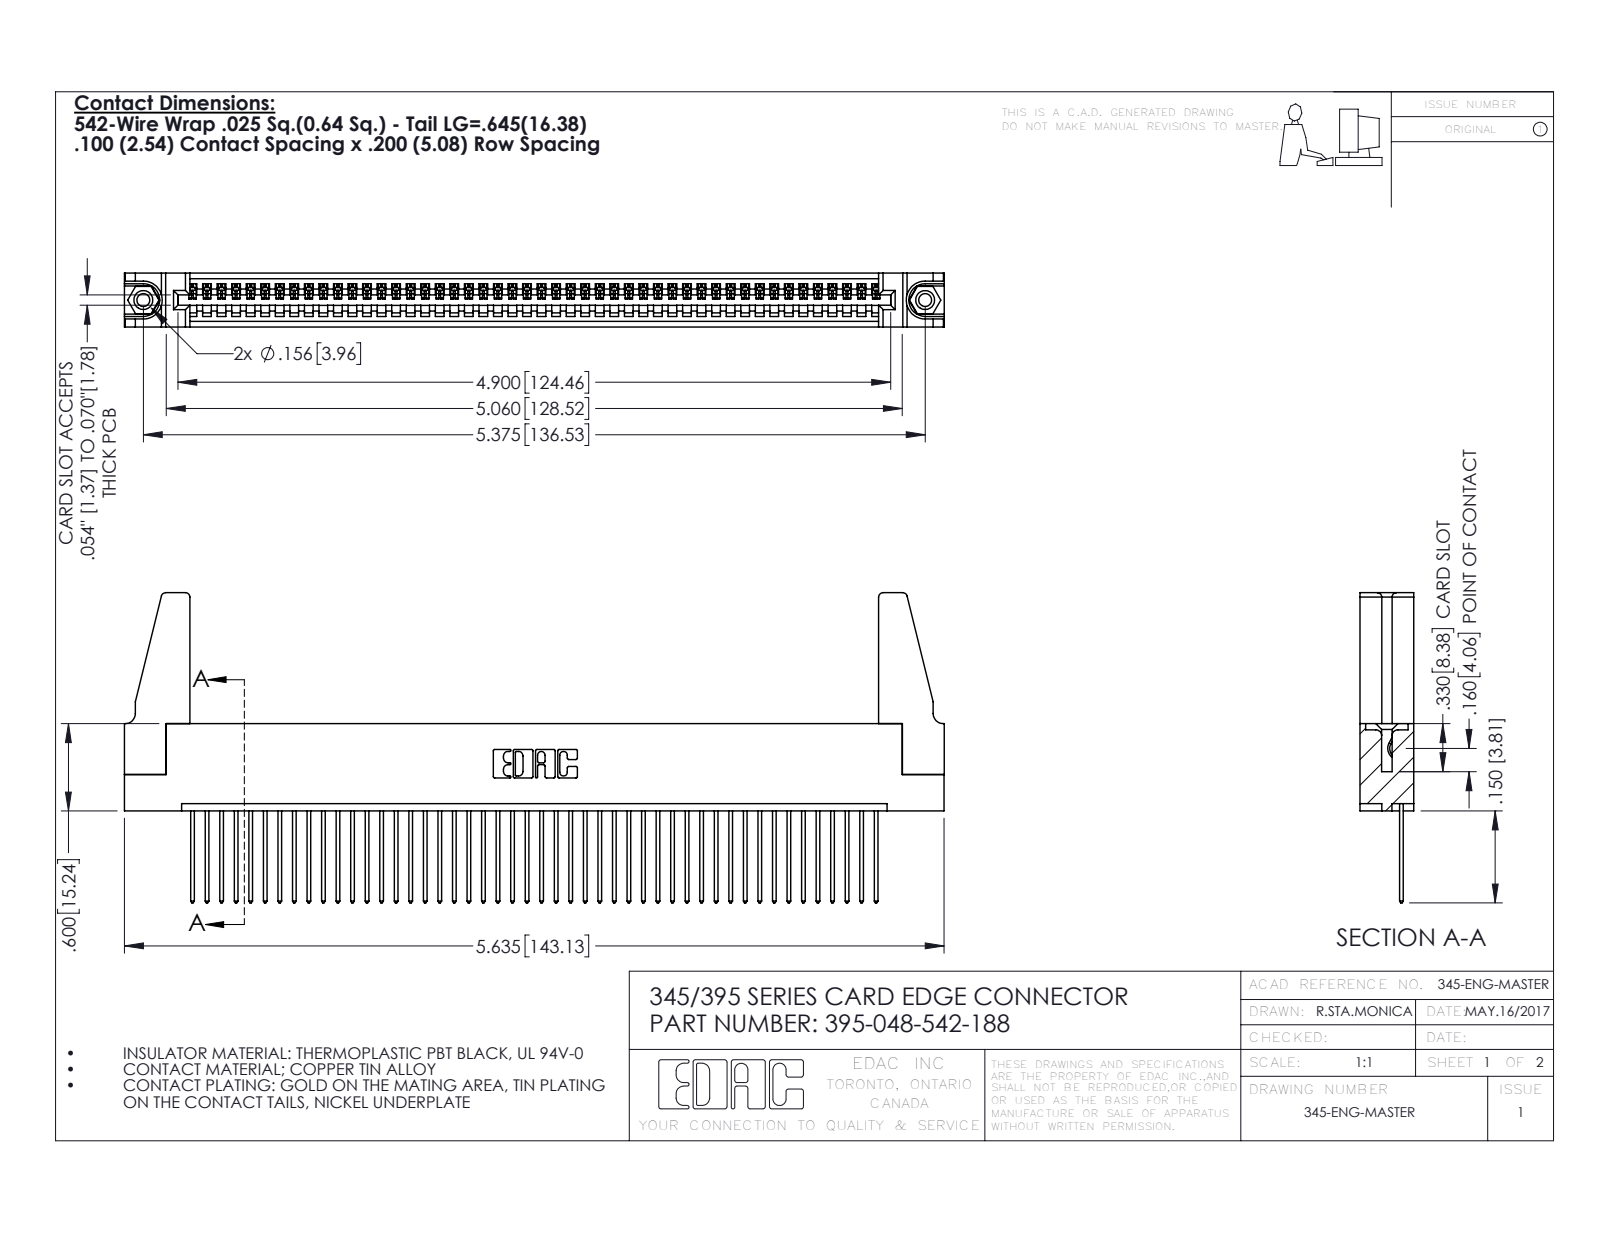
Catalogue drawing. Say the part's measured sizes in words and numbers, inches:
The part is named "345-220-078_345-220-088; 345-292-001_345-293-142; 345 Part_Flush Mounting Lugs - 0.156 Dia-TH; 395-048-542-188 (+1 more)". Its 3-D file was written by "SolidWorks 2016 (CONFIG_CONTROL_DESIGN)". It is 53 solids with 3034 faces: 2072 planar, 946 cylindrical and 16 other. Overall it measures 5.636 by 2.132 by 0.37 inches. Its volume is 1.038 cubic inches and its surface area 34.35 square inches. Round holes: 2 of diameter 0.089, 2 of diameter 0.125, 2 of diameter 0.156, 1 of diameter 0.064. Round bosses or shafts: 2 of diameter 0.155. Partial cylindrical surfaces (rounded edges, fillets, slot ends): 96 of radius 0.006, 96 of radius 0.01, 22 of radius 0.01, 8 of radius 0.03, 6 of radius 0.007, 6 of radius 0.031, 3 of radius 0.026, 2 of radius 0.031. The main face-to-face distances are 0.072, 0.298, 0.37, 0.098, 0.272, 0.025, 0.2, 0.225, 0.149, 0.072. The hole center spacings are 0.27, 5.139, 5.375.
